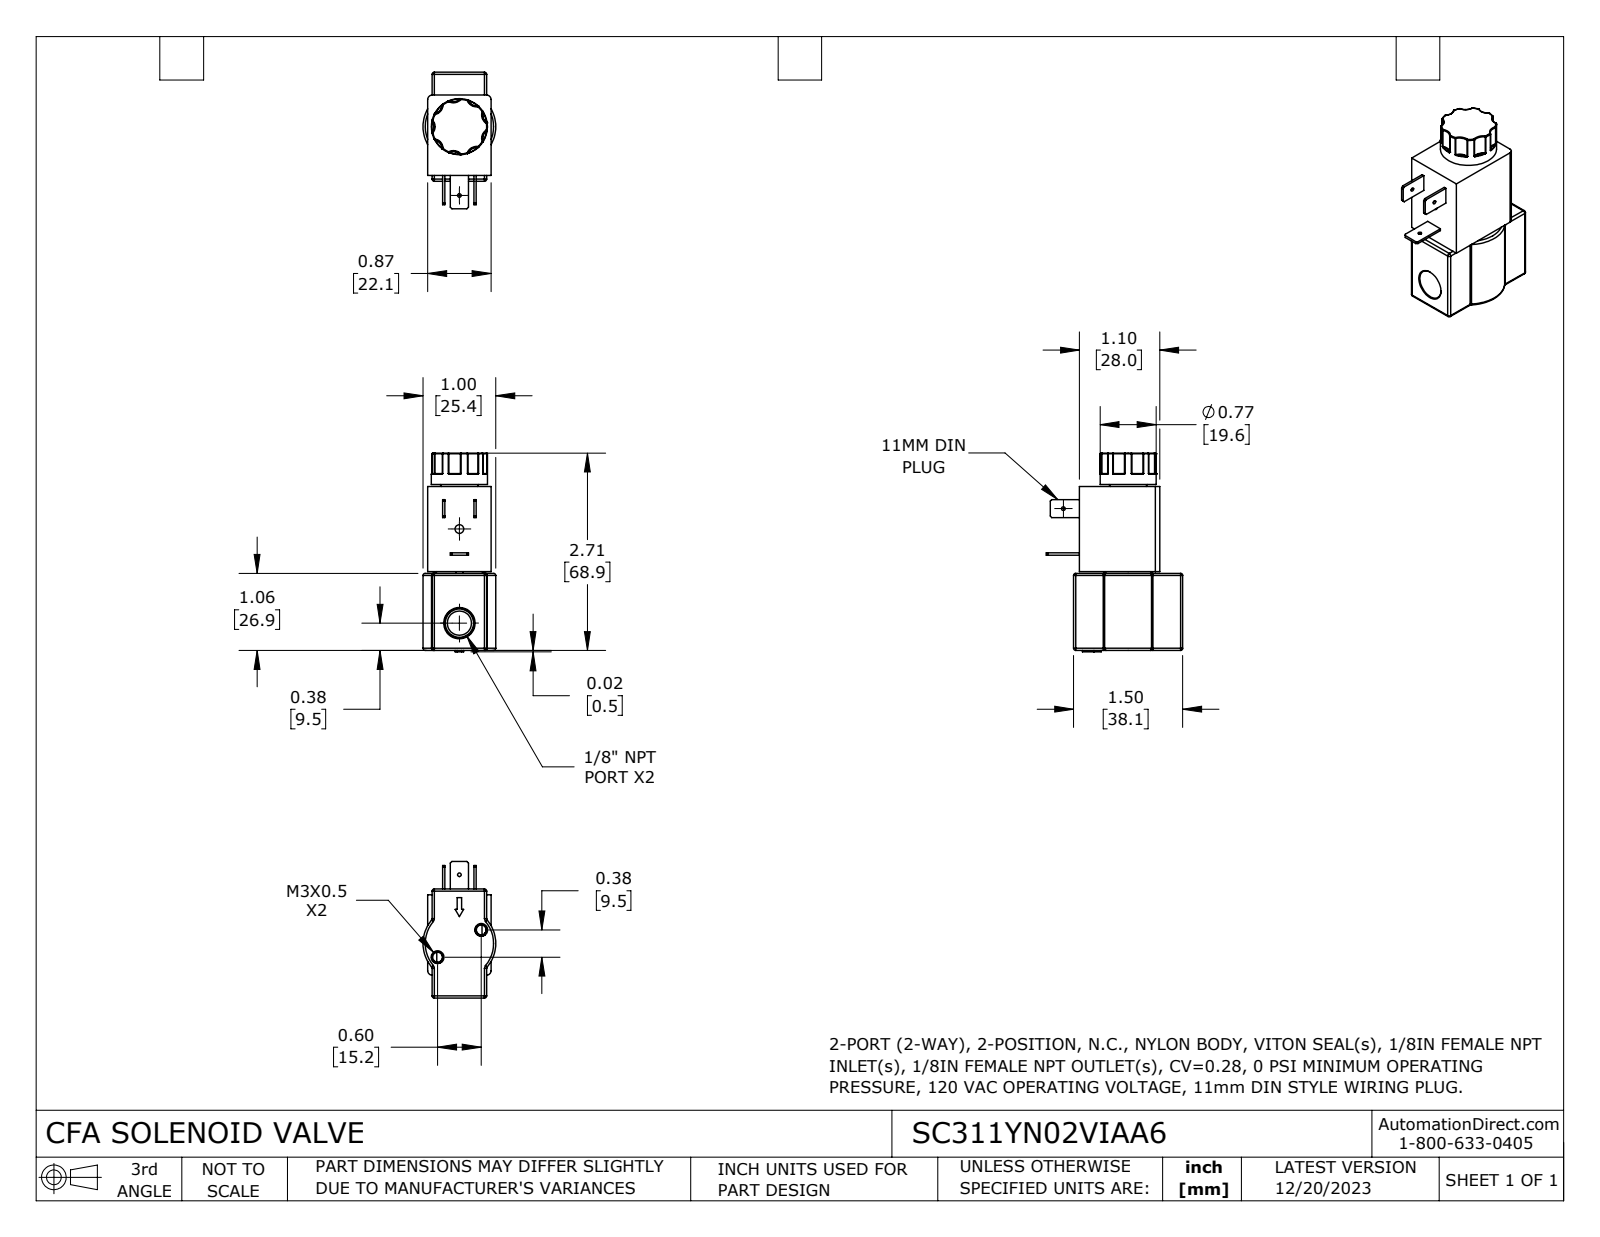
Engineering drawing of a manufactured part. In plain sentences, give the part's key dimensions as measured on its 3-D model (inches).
The part is named "SC311YN02VIAA6". Its 3-D file was written by "SolidWorks 2023 (CONFIG_CONTROL_DESIGN)". It is 1 solid with 383 faces: 62 planar, 117 cylindrical and 204 other. Overall it measures 2.732 by 1.877 by 1 inches. Its volume is 2.516 cubic inches and its surface area 17.12 square inches. Round holes: 2 of diameter 0.05, 2 of diameter 0.136, 1 of diameter 0.12, 1 of diameter 0.332. Round bosses or shafts: 1 of diameter 0.77. Partial cylindrical surfaces (rounded edges, fillets, slot ends): 18 of radius 0.01, 16 of radius 0.03, 7 of radius 0.133, 2 of radius 0.06, 2 of radius 0.132, 2 of radius 0.295, 1 of radius 0.311, 1 of radius 0.5. The main face-to-face distances are 0.06, 0.81, 0.87, 1.104, 2.252, 1.06, 1.192, 0.75, 1.085, 0.025. The hole center spacings are 0.707, 0.815, 1.172, 1.293.
